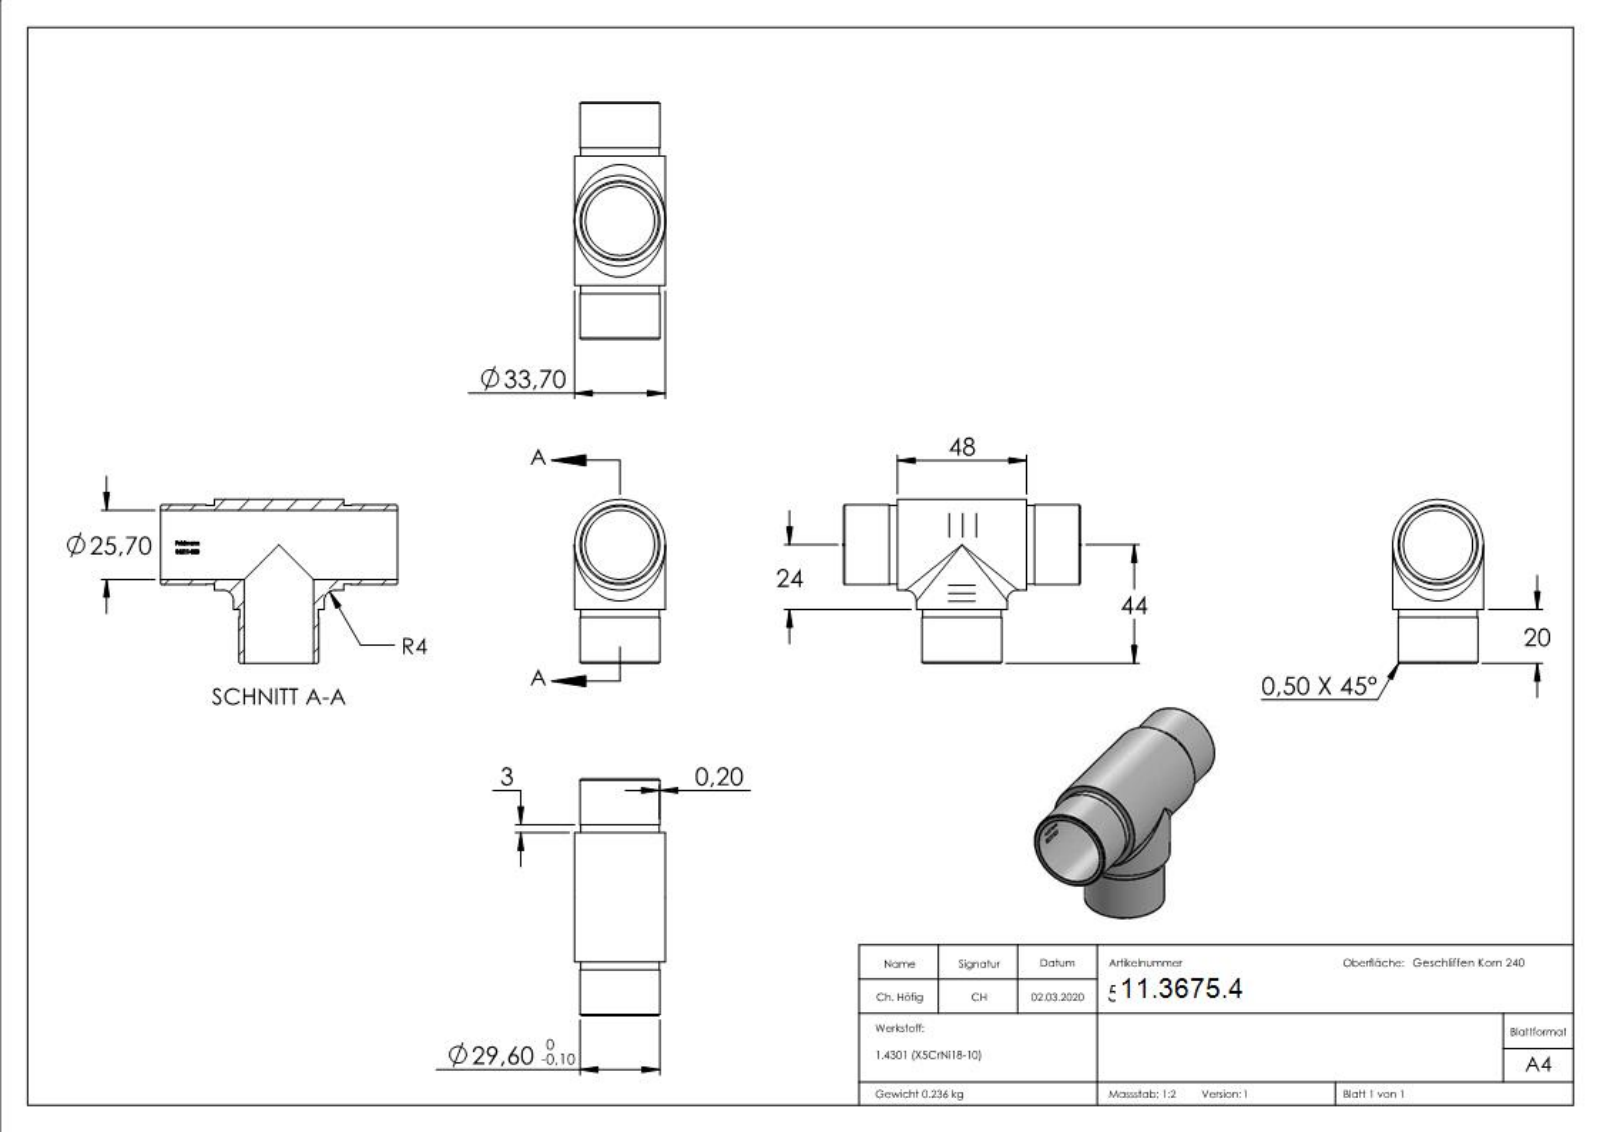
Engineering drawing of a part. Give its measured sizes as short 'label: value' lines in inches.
name: 56211-320
written by: SolidWorks 2015 (CONFIG_CONTROL_DESIGN)
unit: in
bodies: 1 solid, 240 faces (103 planar, 32 cylindrical, 105 other)
size: 3.465 × 2.396 × 1.327
volume: 1.823 in³; area: 33.09 in²
holes: 2× ⌀1.012
bosses: 2× ⌀1.327, 2× ⌀1.165, 2× ⌀1.15
rounds: 1× R0.51
face distances: 0.787, 2.677, 1.89, 3.465, 0.669, 0.118, 2.795, 2.008, 2.126, 0.139
